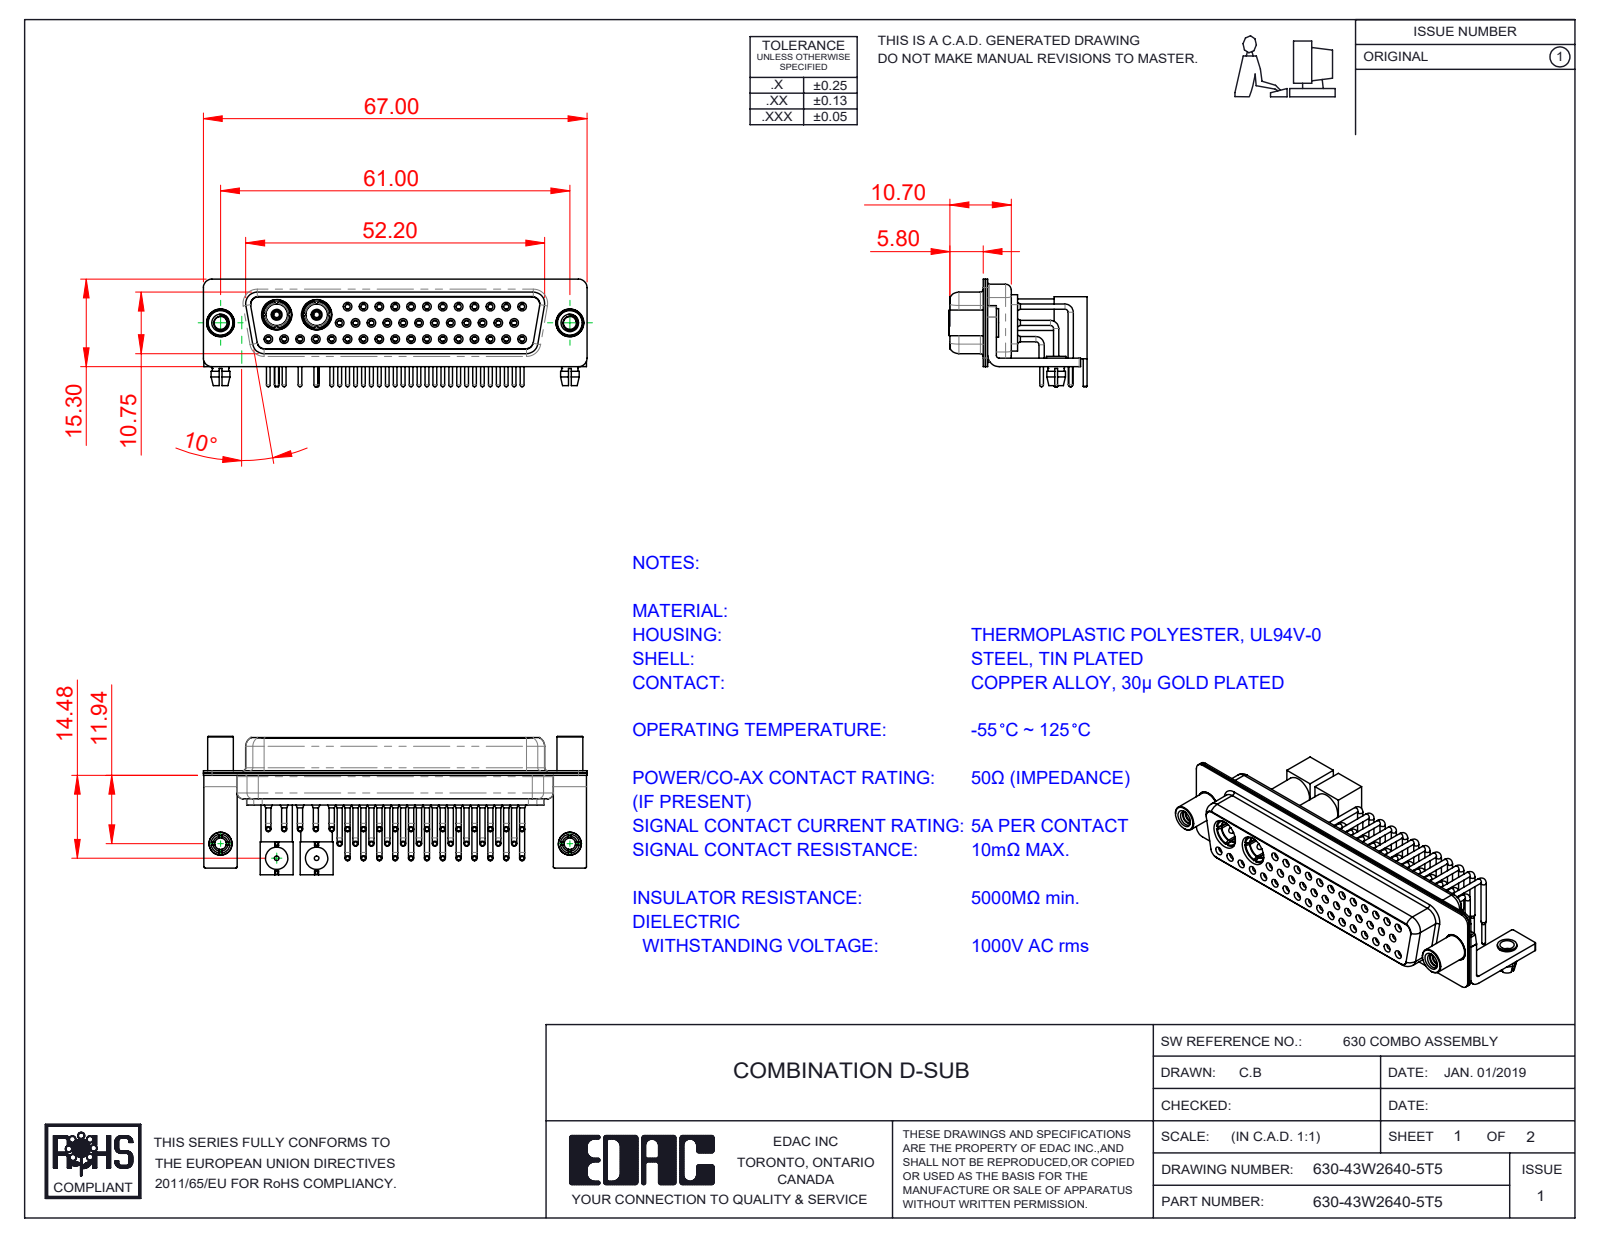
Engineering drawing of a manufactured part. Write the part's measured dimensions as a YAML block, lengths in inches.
part_name: "630Combo Shell Front_50 Contacts; Co-Ax Plug Assy_RA 50; 630Combo Stabilizer Bracket_50 Contacts; Insulator RA Pin (+8 more)"
step_written_by: "SolidWorks 2020 (CONFIG_CONTROL_DESIGN)"
units: inches
bodies: {solids: 62, faces: 2968, planar: 886, cylindrical: 1302, other: 780}
overall_size: [2.638, 0.951, 0.74]
volume: 0.504
surface_area: 28.89
round_holes:
  - {diameter: 0.043, count: 43}
  - {diameter: 0.059, count: 43}
  - {diameter: 0.079, count: 43}
  - {diameter: 0.035, count: 41}
  - {diameter: 0.063, count: 29}
  - {diameter: 0.067, count: 12}
  - {diameter: 0.191, count: 4}
  - {diameter: 0.031, count: 2}
  - {diameter: 0.089, count: 2}
  - {diameter: 0.098, count: 2}
  - {diameter: 0.111, count: 2}
  - {diameter: 0.122, count: 2}
round_bosses_or_shafts:
  - {diameter: 0.035, count: 41}
  - {diameter: 0.026, count: 41}
  - {diameter: 0.063, count: 12}
  - {diameter: 0.197, count: 4}
  - {diameter: 0.157, count: 4}
  - {diameter: 0.114, count: 4}
  - {diameter: 0.217, count: 2}
  - {diameter: 0.205, count: 2}
partial_cylinders:
  - {radius: 0.01, count: 16}
  - {radius: 0.059, count: 16}
  - {radius: 0.079, count: 13}
  - {radius: 0.053, count: 12}
  - {radius: 0.063, count: 8}
  - {radius: 0.02, count: 5}
  - {radius: 0.024, count: 4}
  - {radius: 0.026, count: 4}
face_to_face_distances: [0.016, 0.031, 0.236, 0.22, 0.059, 0.228, 0.205, 0.444, 0.072, 0.407]
hole_center_spacings: [0.109, 0.124, 0.218, 0.327, 0.436, 0.545, 0.654, 0.763]
